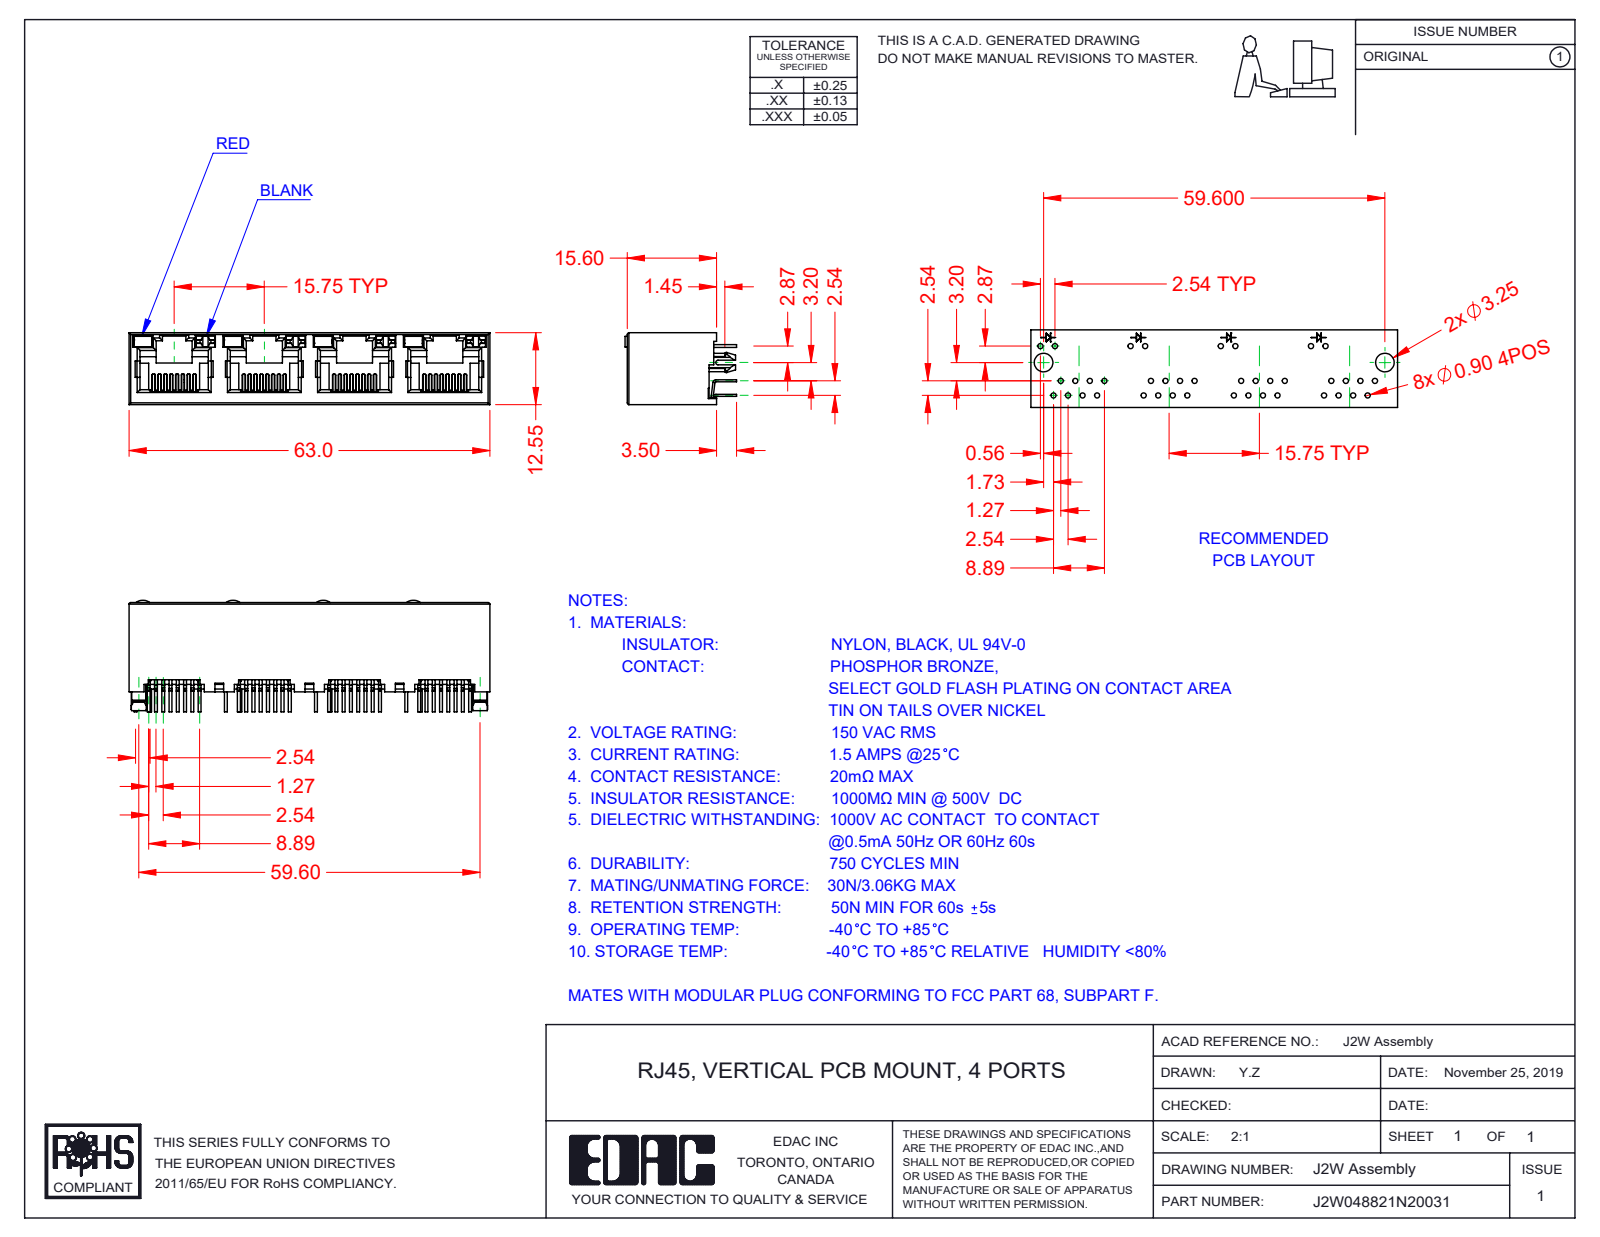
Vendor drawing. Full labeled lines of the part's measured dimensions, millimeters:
Part name (STEP PRODUCT): 2W Insulator; 2W Contact Lock; 2W LED RH_0-Blank; 2W LED LH_2-Red (+2 more)
STEP written by: SolidWorks 2020 (CONFIG_CONTROL_DESIGN)
Units: millimetres
Bodies: 41 solids, 3007 faces (2508 planar, 441 cylindrical, 58 other)
Overall size (bounding box): 63 × 19.5 × 12.55
Volume: 5 212 mm³ · Surface area: 12 695 mm²
Partial cylindrical surfaces — rounded edges, fillets, slot ends (radius × count): R0.15 ×64, R0.2 ×29, R0.5 ×28, R0.3 ×14, R0.45 ×8, R2 ×4, R0.25 ×2, R1.5 ×2
Main face-to-face distances: 12.55, 11.9, 0.65, 15.75, 0.36, 1.5, 0.78, 0.6, 11.3, 31.5
